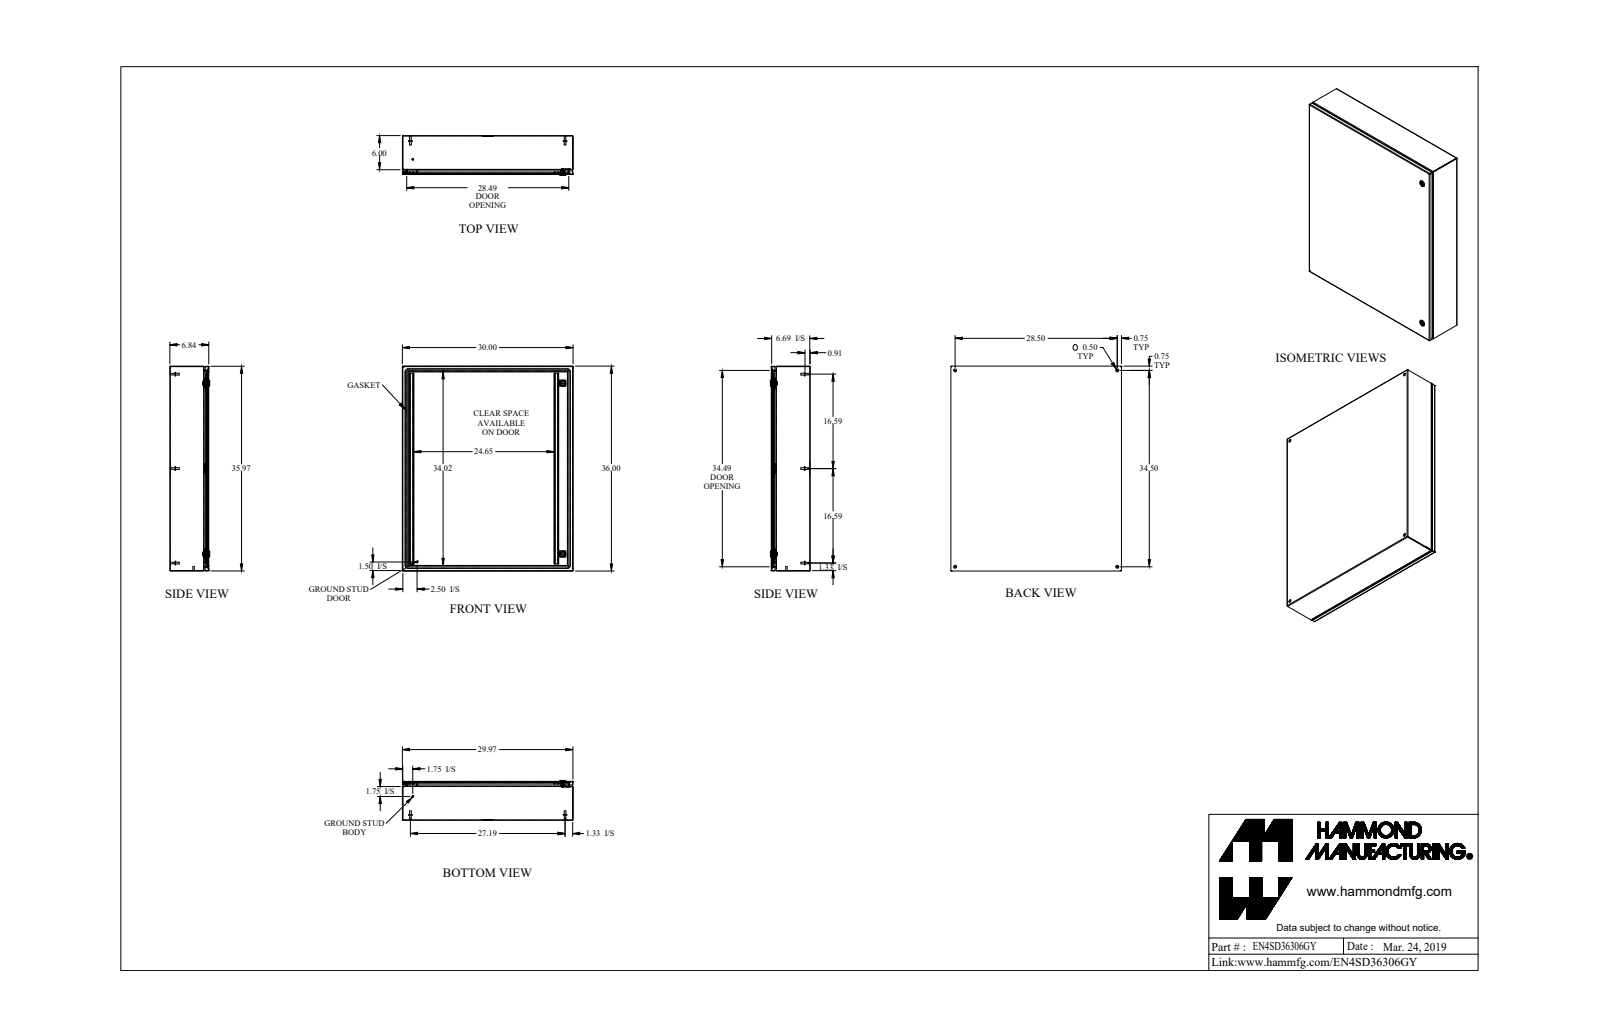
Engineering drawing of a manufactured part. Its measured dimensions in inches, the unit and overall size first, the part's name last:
Units: inches
Overall size (bounding box): 36 × 30 × 6.997
Round holes (diameter × count): ⌀0.5 ×4, ⌀0.232 ×2, ⌀0.625 ×2, ⌀0.785 ×2, ⌀0.172 ×1, ⌀0.24 ×1, ⌀0.242 ×1
Round bosses / shafts (diameter × count): ⌀0.625 ×6, ⌀0.313 ×6, ⌀0.27 ×6, ⌀1.1 ×2, ⌀0.525 ×2, ⌀0.281 ×2, ⌀0.25 ×2, ⌀0.455 ×1
Partial cylindrical surfaces — rounded edges, fillets, slot ends (radius × count): R0.036 ×20, R0.108 ×20, R0.043 ×12, R0.081 ×12, R0.312 ×10, R0.006 ×6, R0.062 ×6, R0.125 ×4
Main face-to-face distances: 0.072, 6.765, 6.693, 6.837, 29.928, 35.928, 29.856, 30, 35.856, 36
Hole centre spacings: 27.519, 28.5, 34.5, 44.749, 2.493, 2.494, 29.999, 32.267
Volume: 248.7 in³ · Surface area: 6 974 in²
Bodies: 33 solids, 909 faces (430 planar, 295 cylindrical, 184 other)
Part name (STEP PRODUCT): EN4SD36306GY_Default
STEP written by: SolidWorks 2019 (CONFIG_CONTROL_DESIGN)
